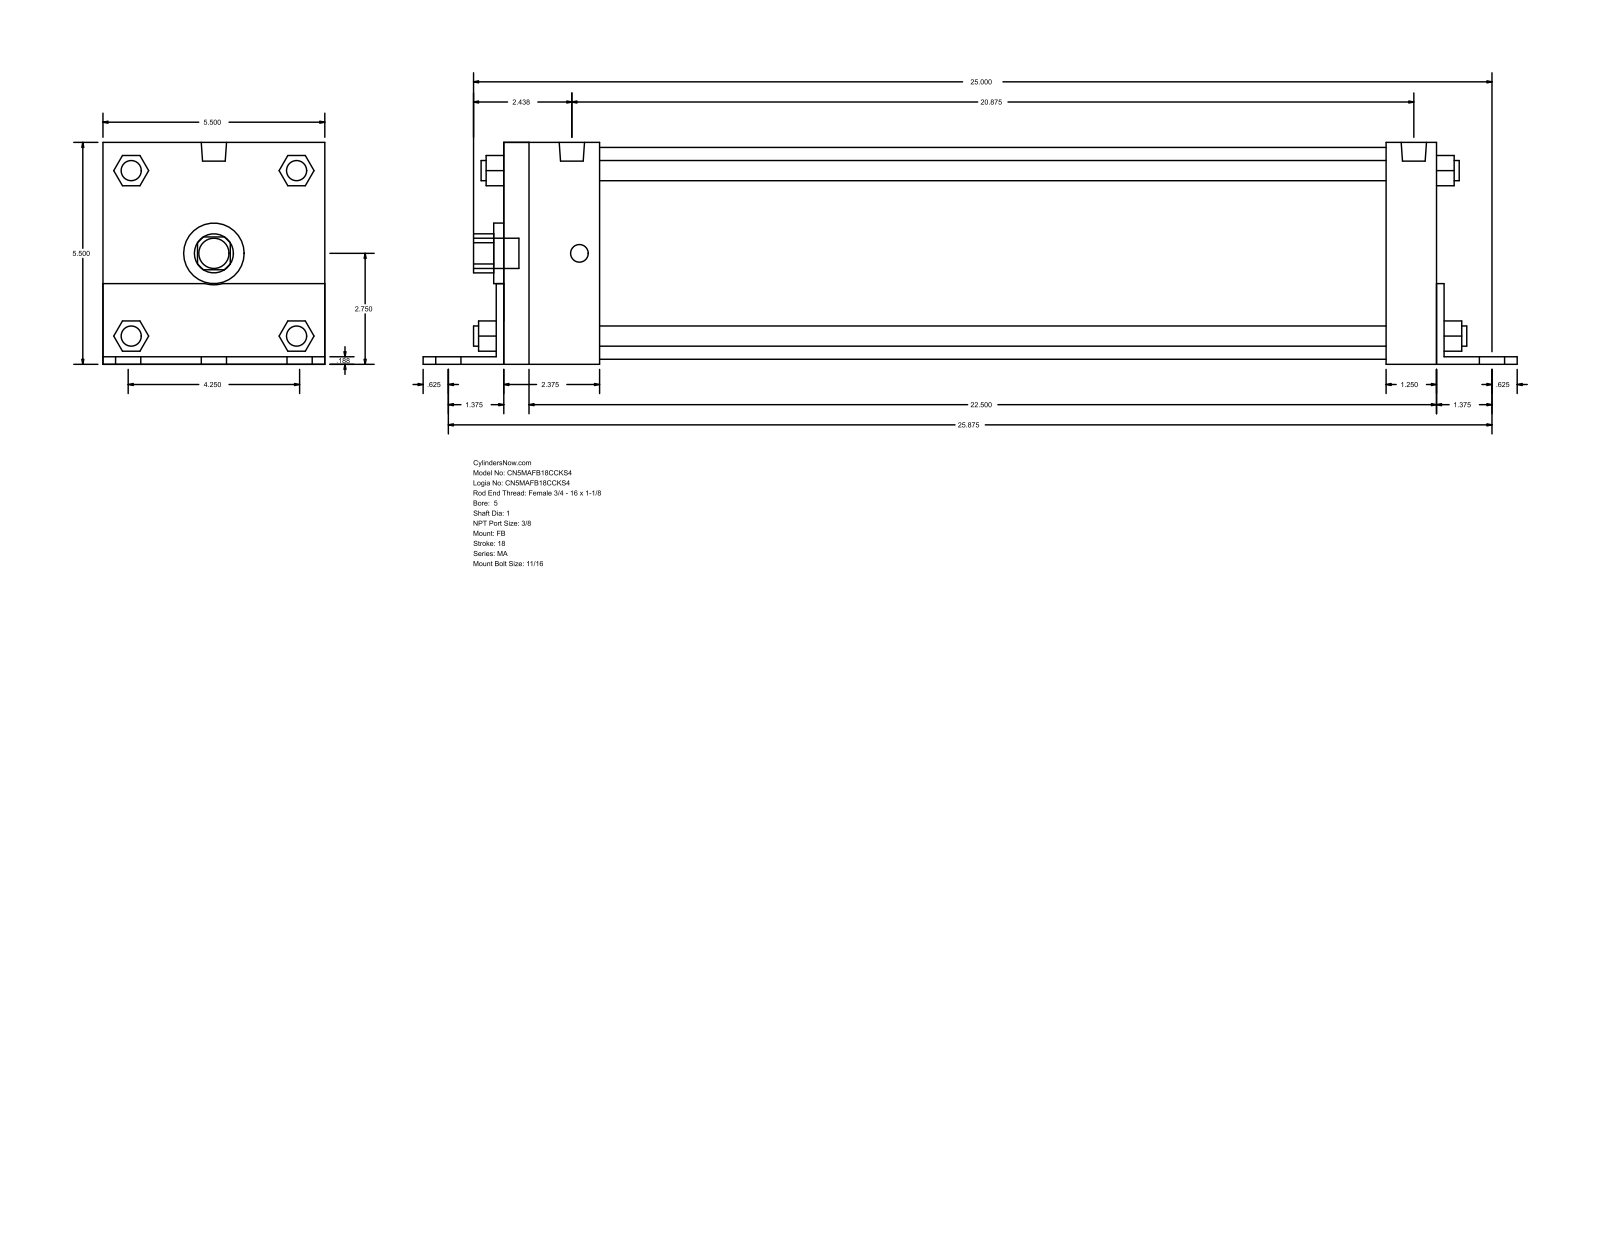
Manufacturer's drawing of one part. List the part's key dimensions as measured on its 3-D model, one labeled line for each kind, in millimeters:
Part name (STEP PRODUCT): MA_FB__0500_1
STEP written by: GSSL Pune (CONFIG_CONTROL_DESIGN)
Units: millimetres
Bodies: 0 solids, 140 faces (105 planar, 35 cylindrical, 0 other)
Overall size (bounding box): 688.98 × 139.75 × 139.7
Round holes (diameter × count): ⌀25.4 ×1, ⌀38.1 ×1, ⌀133.35 ×1
Round bosses / shafts (diameter × count): ⌀17.46 ×6, ⌀12.7 ×4, ⌀11.11 ×4, ⌀15.93 ×2, ⌀19.05 ×1
Partial cylindrical surfaces — rounded edges, fillets, slot ends (radius × count): R12.29 ×1, R19.81 ×1
Main face-to-face distances: 139.7, 4.76, 139.75, 4.71, 134.99, 587.37, 4.77, 592.14, 592.13, 596.9
